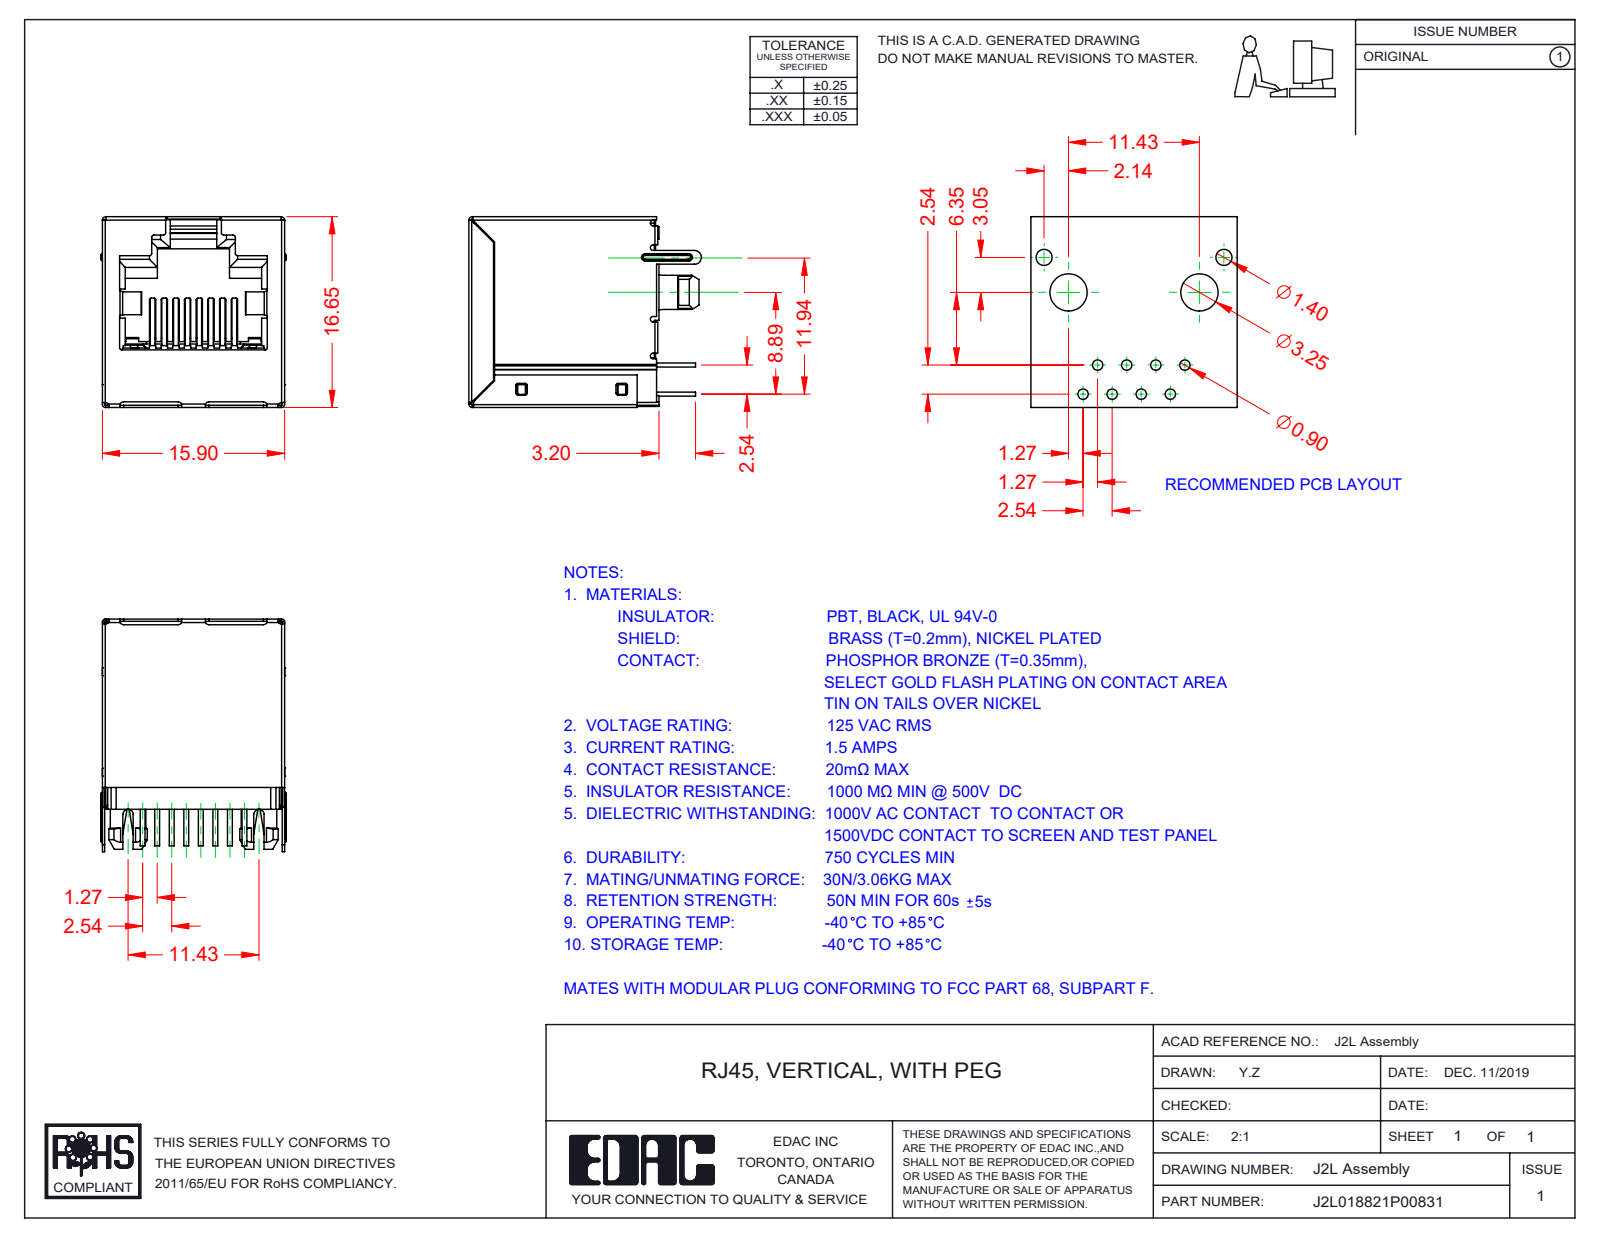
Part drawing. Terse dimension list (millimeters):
name: RJ2L018821P00831; 2L Contacts; 2L Insulator; 2L Mylar Tape (+2 more)
written by: SolidWorks 2016 (CONFIG_CONTROL_DESIGN)
unit: mm
bodies: 12 solids, 1131 faces (784 planar, 284 cylindrical, 63 other)
size: 20.3 × 16.65 × 16.2
volume: 2 735 mm³; area: 6 843 mm²
bosses: 2× ⌀3.1, 2× ⌀1.1
rounds: 64× R0.15, 20× R0.25, 16× R0.2, 14× R0.3, 9× R0.35, 8× R0.1, 4× R0.28, 3× R0.5
face distances: 15.45, 15.7, 16.45, 16.2, 16.4, 15.65, 16.3, 16.25, 15.9, 15.5
